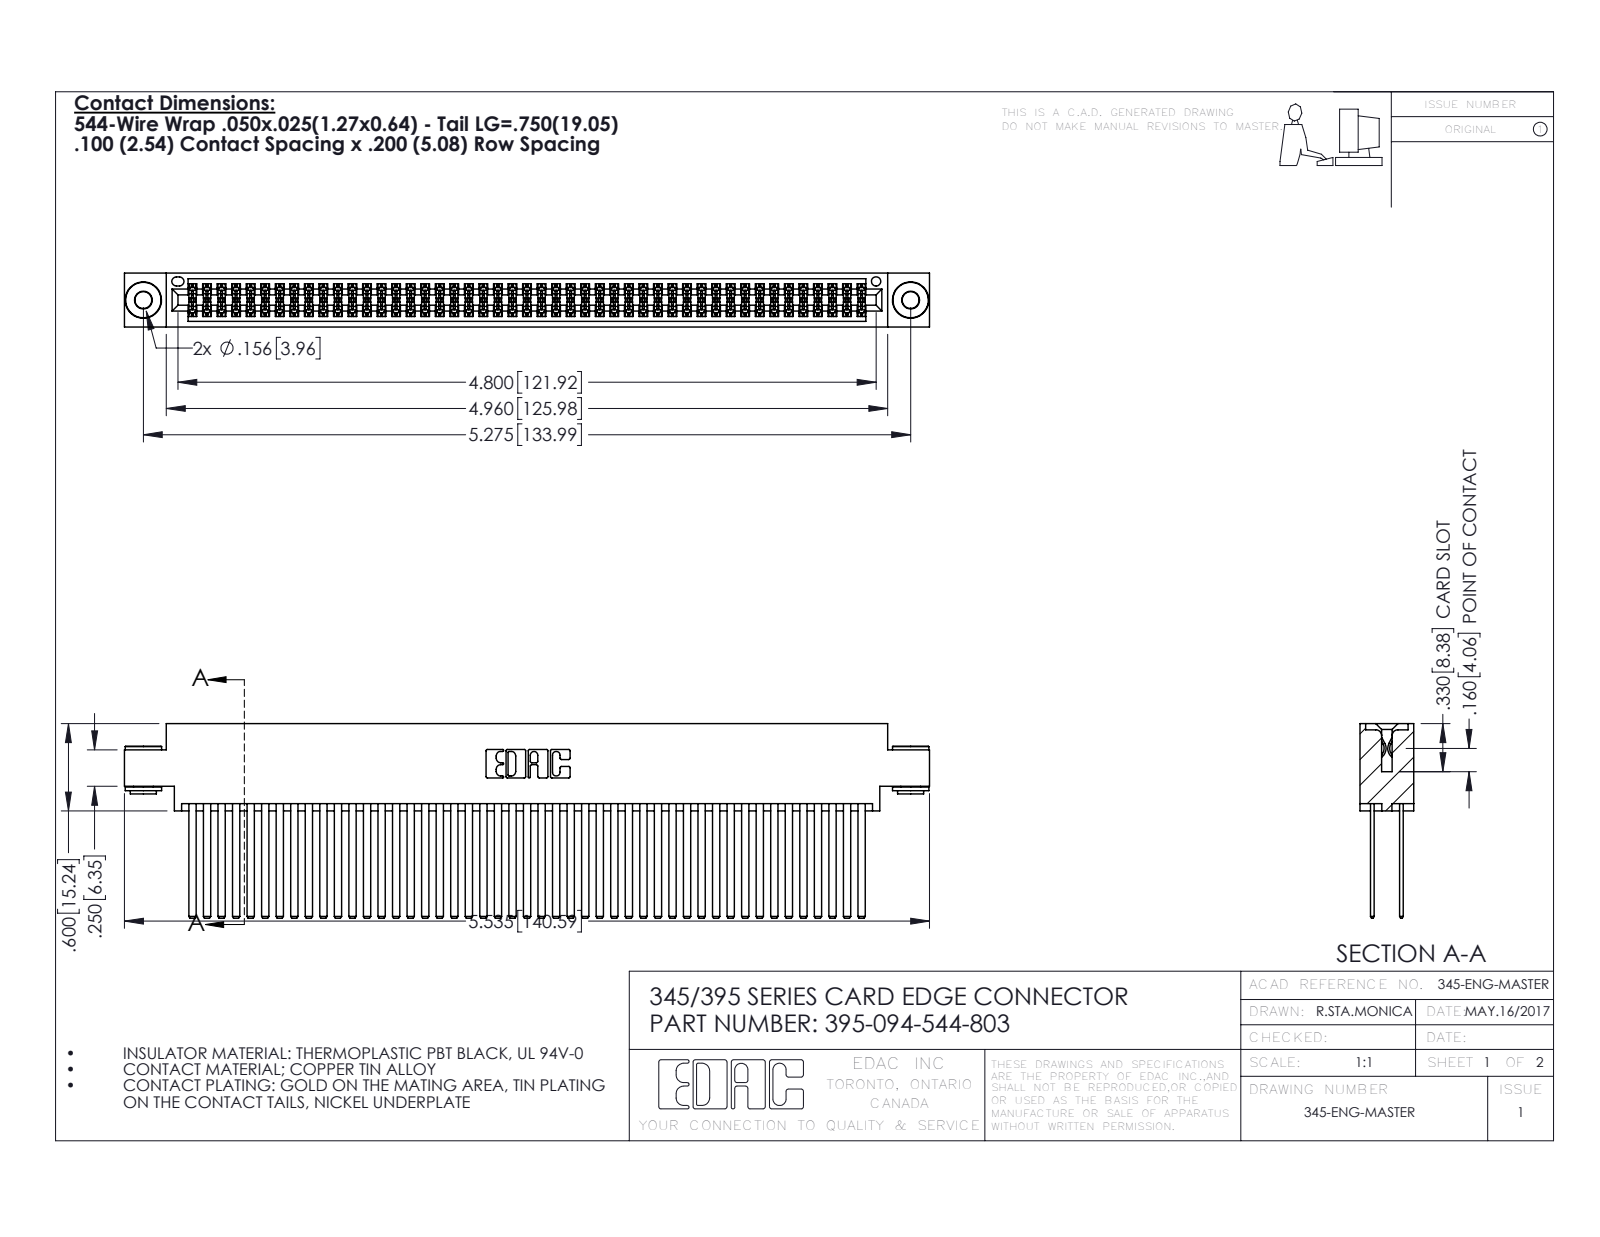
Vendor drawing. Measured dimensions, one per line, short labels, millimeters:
name: 345-250-002_345-250-002-102; 345-292-001_345-293-144; 345 Part_0.170 Offset - 0.156 Dia-TH; 395-094-544-803
written by: SolidWorks 2016 (CONFIG_CONTROL_DESIGN)
unit: mm
bodies: 97 solids, 4304 faces (2820 planar, 1476 cylindrical, 8 other)
size: 140.6 × 34 × 9.4
volume: 14 900 mm³; area: 26 370 mm²
holes: 2× ⌀2.9, 2× ⌀4, 1× ⌀1.6
bosses: 2× ⌀6.4, 2× ⌀4.6, 2× ⌀3.5
rounds: 141× R0.2, 22× R0.3, 6× R0.2, 6× R0.8, 3× R0.7, 2× R0.4, 2× R0.5, 2× R0.6
face distances: 5.1, 0.6, 1.8, 2.5, 6.9, 7.6, 5.7, 4.4, 9.4, 3.8
hole spacings: 6.9, 128, 134
